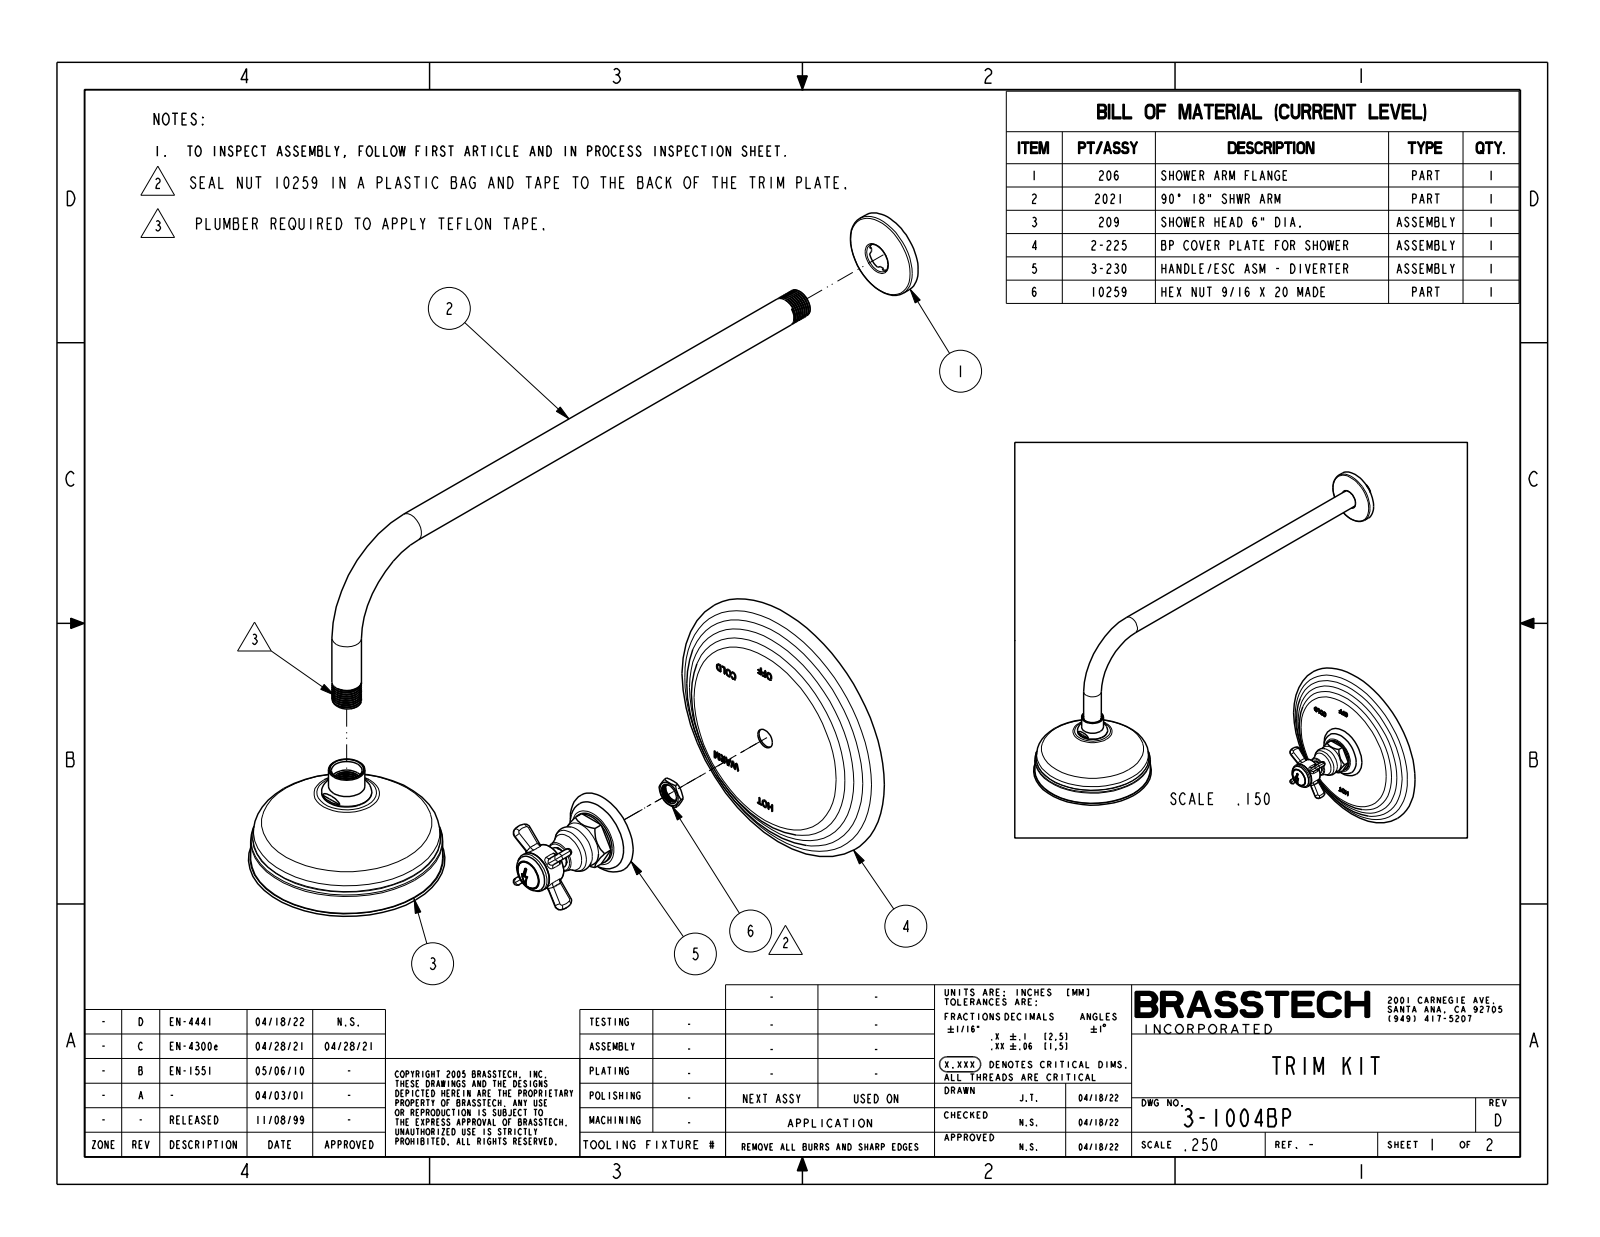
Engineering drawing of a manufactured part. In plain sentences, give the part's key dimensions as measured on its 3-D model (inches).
The part is named "3-1004BP". Its 3-D file was written by "CREO PARAMETRIC BY PTC INC, 2018400 (CONFIG_CONTROL_DESIGN)". It is 2 solids with 1038 faces: 332 planar, 196 cylindrical and 510 other. Overall it measures 20.065 by 19.701 by 7.75 inches. Its volume is 70.89 cubic inches and its surface area 256.6 square inches. Round holes: 76 of diameter 0.02, 1 of diameter 5.236. Round bosses or shafts: 2 of diameter 0.813, 1 of diameter 5.276, 1 of diameter 2.38, 1 of diameter 1.482, 1 of diameter 1.375, 1 of diameter 1.1, 1 of diameter 1, 1 of diameter 0.99. Partial cylindrical surfaces (rounded edges, fillets, slot ends): 12 of radius 0.1. The main face-to-face distances are 0.754, 0.02, 0.2, 1.914, 1.894, 2.811, 2.057, 1.313, 2.441, 1.687. The hole center spacings are 1.417, 0.945, 1.153, 2.455, 0.472, 0.589, 1.18, 1.356.
